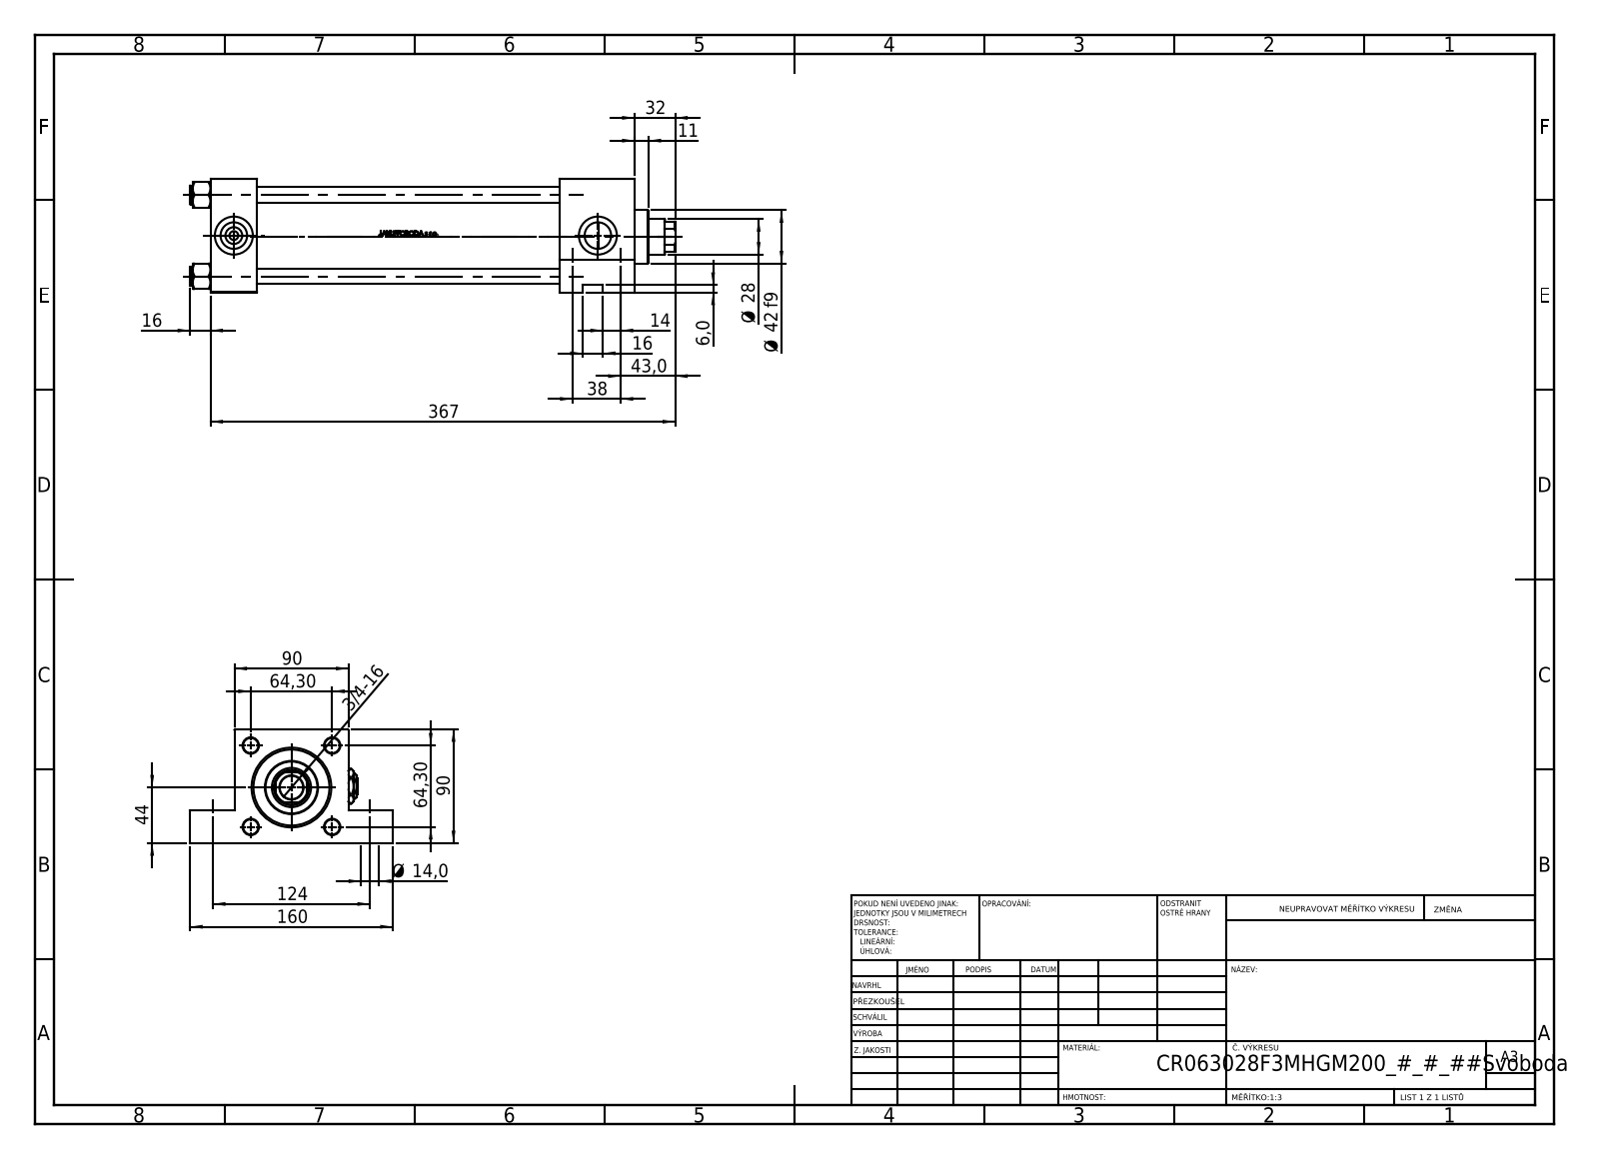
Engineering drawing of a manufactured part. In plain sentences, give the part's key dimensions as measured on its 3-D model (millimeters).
The part is named "V215CR_VCP_F; V215CR_F_Body; Zatka_pro_OIL_PORT; NUT_M5_F (+2 more)". Its 3-D file was written by "SolidWorks 2019 (CONFIG_CONTROL_DESIGN)". It is 13 solids with 1200 faces: 484 planar, 134 cylindrical and 582 other. Overall it measures 383 by 160 by 90 millimeters. Its volume is 1 327 000 cubic millimeters and its surface area 316 279 square millimeters. Round holes: 4 of diameter 12, 4 of diameter 14, 3 of diameter 20.96, 3 of diameter 30, 2 of diameter 7, 1 of diameter 18.5, 1 of diameter 20, 1 of diameter 28, 1 of diameter 31, 1 of diameter 50, 1 of diameter 60, 1 of diameter 63. Round bosses or shafts: 4 of diameter 15, 1 of diameter 69, 1 of diameter 42. Partial cylindrical surfaces (rounded edges, fillets, slot ends): 1 of radius 13.5. The main face-to-face distances are 90, 37, 298, 335, 59, 276, 239, 26, 64, 306.3. The hole center spacings are 64.3, 38, 44.77, 46.18, 90.93, 124, 129.69, 10.
